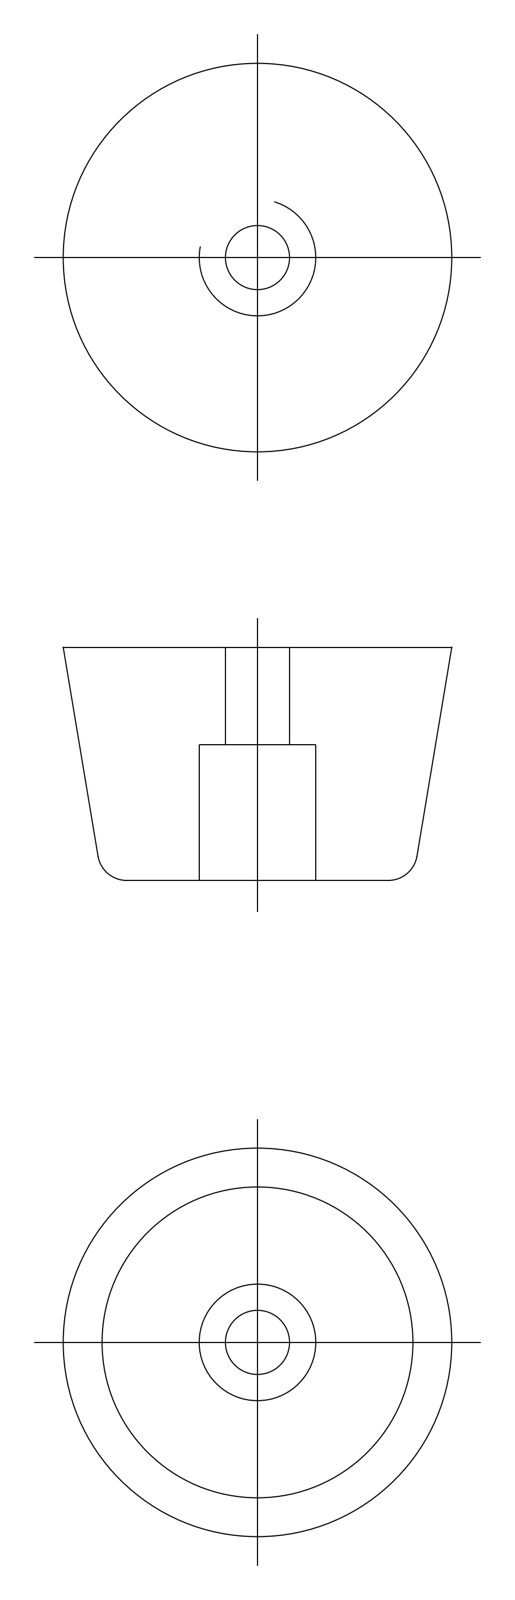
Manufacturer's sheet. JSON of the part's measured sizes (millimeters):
{"step_written_by": "spGate 19.8.4 (****-****-****-****) (AUTOMOTIVE_DESIGN)", "units": "millimeters", "bodies": {"solids": 1, "faces": 11, "planar": 3, "cylindrical": 4, "other": 4}, "overall_size": [20, 20, 12], "volume_mm3": 2816, "surface_area_mm2": 1348, "round_holes": [[3.3, 1], [6, 1]], "face_to_face_distances": [12, 7, 5]}
